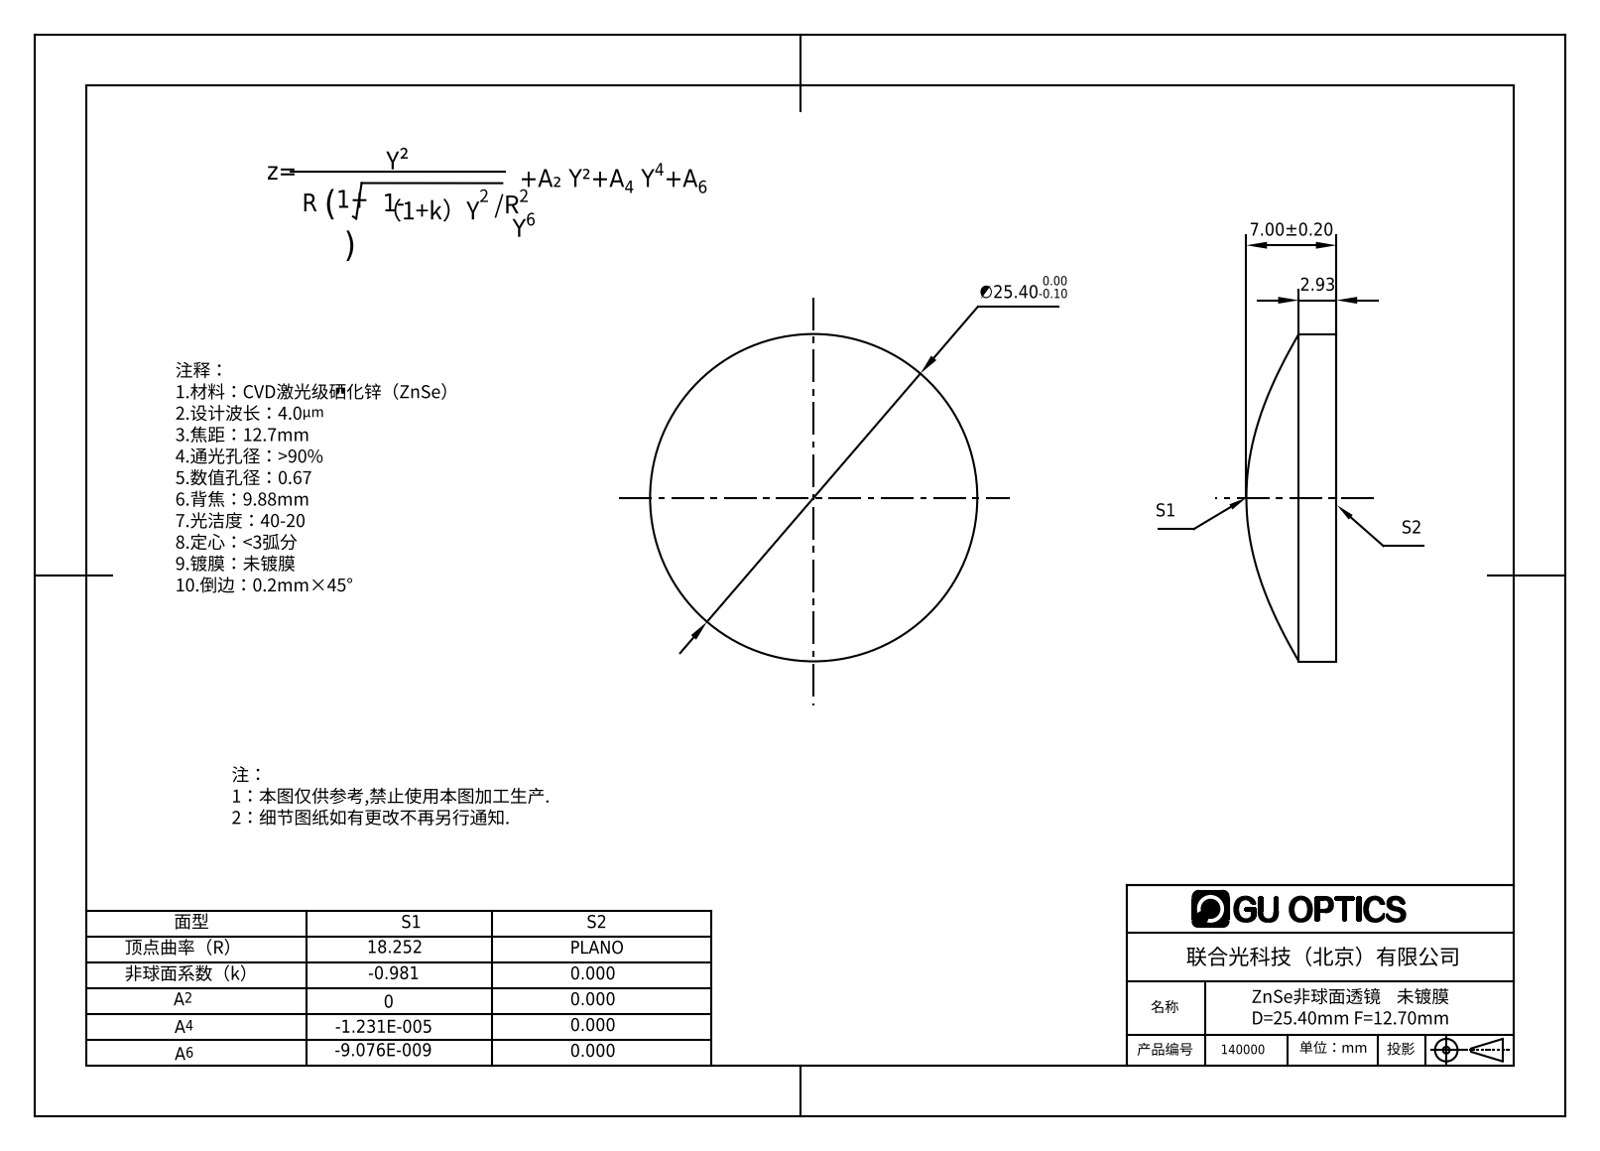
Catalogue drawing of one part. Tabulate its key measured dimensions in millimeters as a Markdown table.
| quantity | value |
| --- | --- |
| part name | GL7AL1-025-012 |
| STEP written by | SolidWorks 2022 (AUTOMOTIVE_DESIGN) |
| units | millimeters |
| bodies | 1 solid, 11 faces (1 planar, 2 cylindrical, 8 other) |
| overall size | 25.4 × 25.4 × 7 |
| volume | 2 371 mm³ |
| surface area | 1 275 mm² |
| round bosses / shafts (diameter × count) | 25.4 × 1 |
